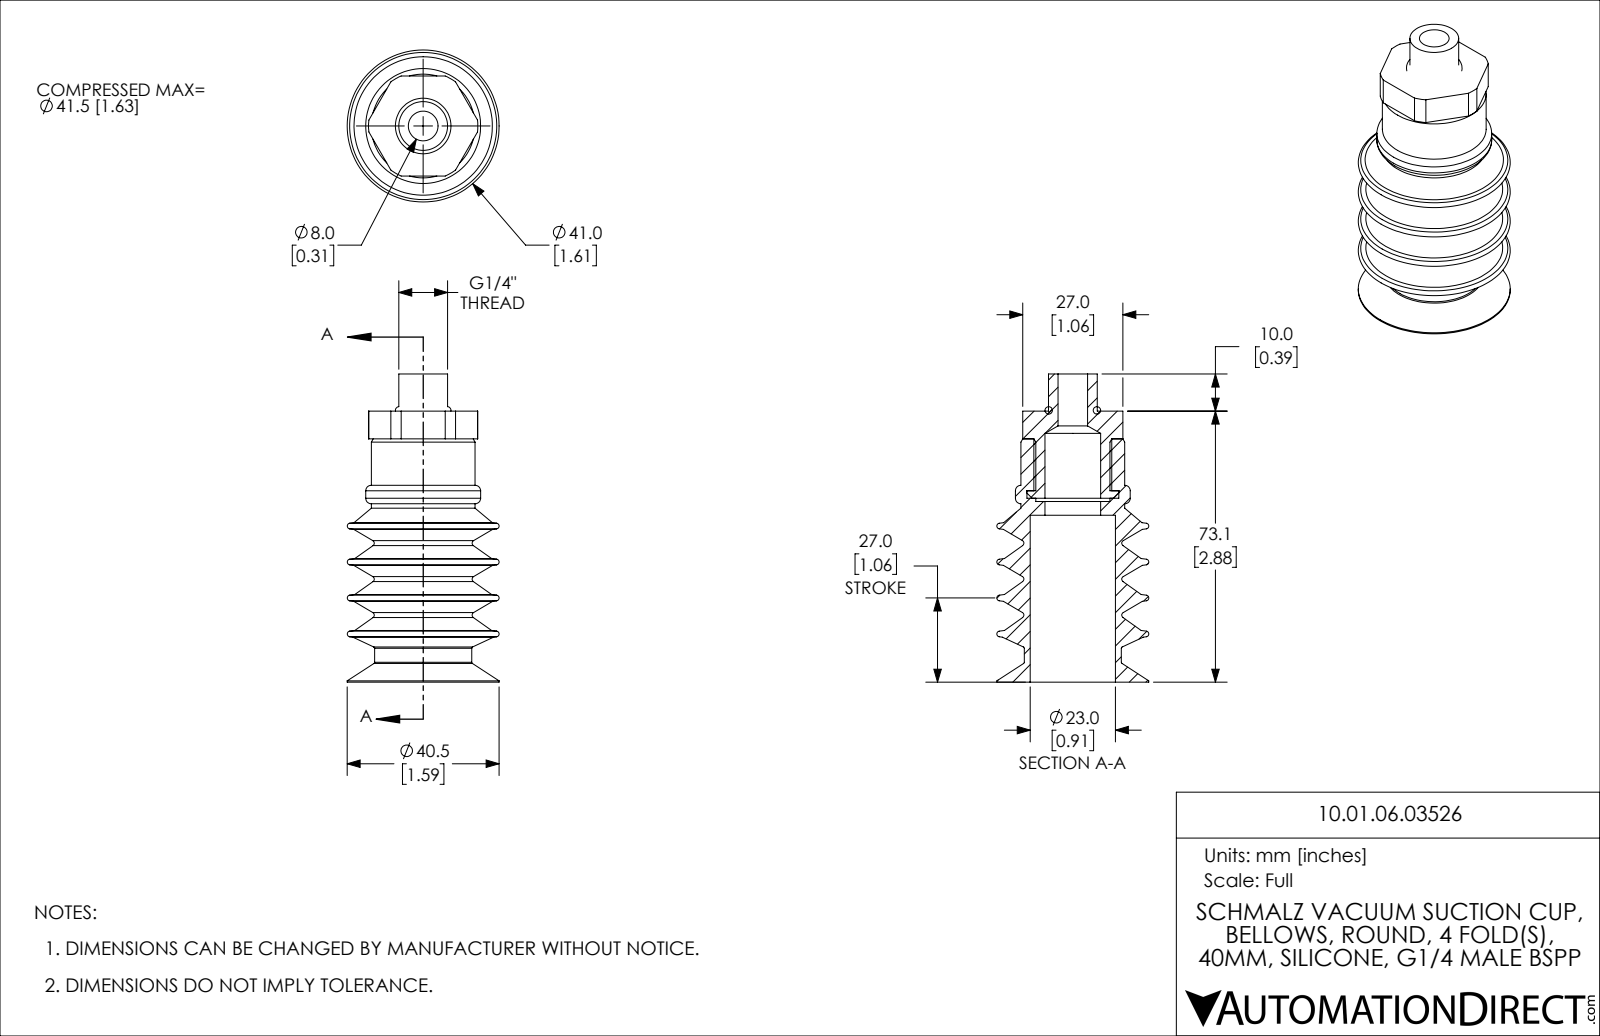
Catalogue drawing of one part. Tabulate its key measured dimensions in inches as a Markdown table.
| quantity | value |
| --- | --- |
| part name | 10.01.06.03526 |
| STEP written by | SolidWorks 2021 (CONFIG_CONTROL_DESIGN) |
| units | inches |
| bodies | 3 solids, 128 faces (17 planar, 37 cylindrical, 74 other) |
| overall size | 3.272 × 1.614 × 1.614 |
| volume | 2.144 in³ |
| surface area | 34.28 in² |
| round holes (diameter × count) | 0.315 × 1, 0.591 × 1, 0.787 × 1, 0.906 × 1, 0.976 × 1 |
| round bosses / shafts (diameter × count) | 1.614 × 1, 1.22 × 1, 1.102 × 1, 1.031 × 1, 0.984 × 1, 0.827 × 1, 0.518 × 1 |
| partial cylindrical surfaces (radius × count) | 0.581 × 1 |
| main face-to-face distances | 2.583, 2.878, 0.295, 1.953, 0.63, 0.925, 2.031, 0.079, 0.551, 0.846 |
